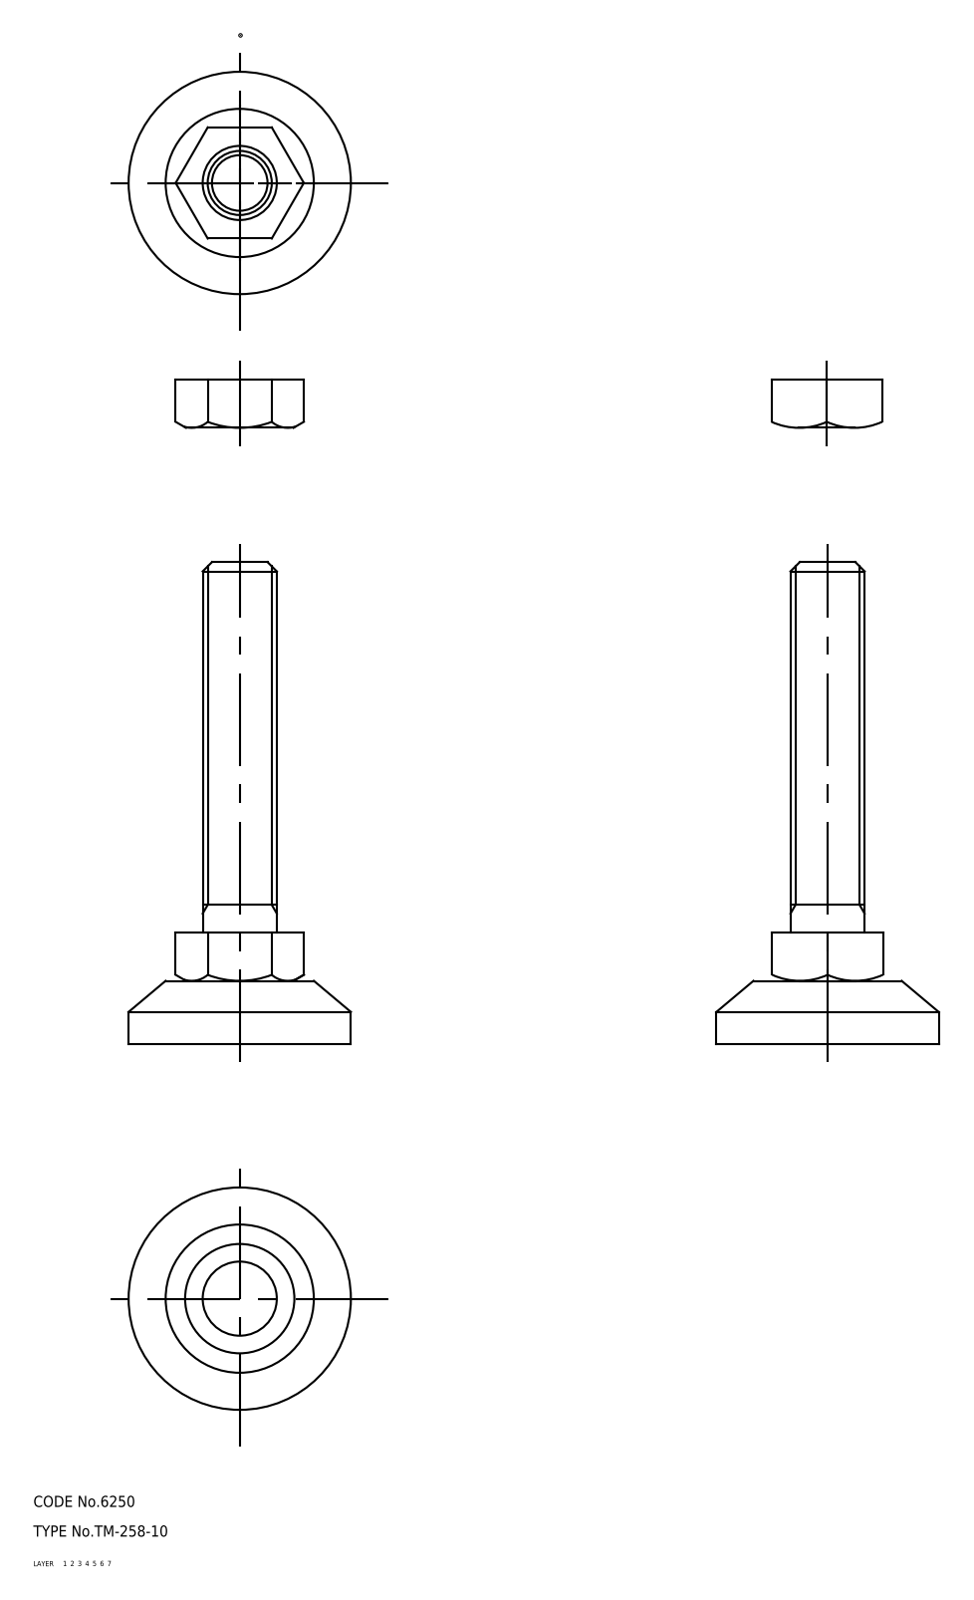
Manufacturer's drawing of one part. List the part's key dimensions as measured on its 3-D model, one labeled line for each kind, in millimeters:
Part name (STEP PRODUCT): 67112382; 67112395; 67112408
STEP written by: CADfix (AUTOMOTIVE_DESIGN)
Units: millimetres
Bodies: 3 solids, 67 faces (0 planar, 0 cylindrical, 67 other)
Overall size (bounding box): 130 × 60 × 60
Volume: 79 993 mm³ · Surface area: 21 577 mm²
